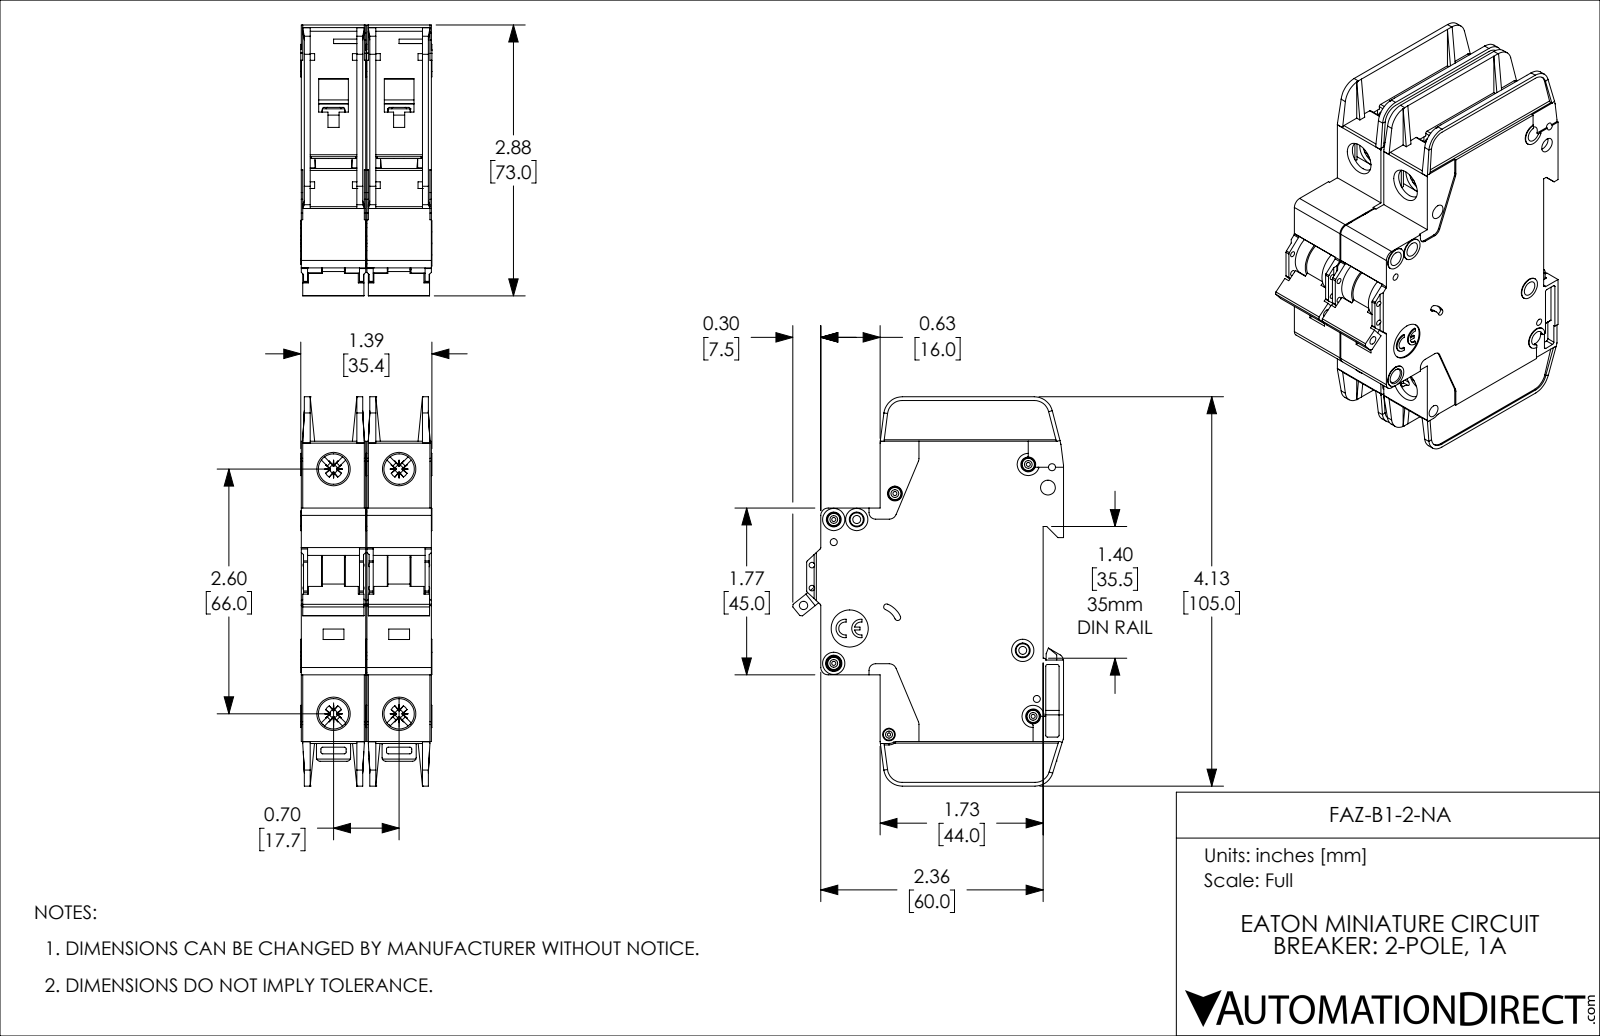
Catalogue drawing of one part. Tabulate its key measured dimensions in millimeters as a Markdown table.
| quantity | value |
| --- | --- |
| part name | FAZ-B1-2-NA |
| STEP written by | SolidWorks 2019 (AUTOMOTIVE_DESIGN) |
| units | millimeters |
| bodies | 2 solids, 2254 faces (1342 planar, 714 cylindrical, 198 other) |
| overall size | 105 × 73.1 × 35.4 |
| volume | 153 500 mm³ |
| surface area | 52 910 mm² |
| round holes (diameter × count) | 4 × 8, 1.1 × 5, 1.9 × 4, 8.2 × 4, 1.5 × 2, 2.2 × 2, 0.9 × 1, 2.3 × 1, 2.5 × 1, 3.4 × 1, 10 × 1 |
| round bosses / shafts (diameter × count) | 3.3 × 5, 6 × 4, 3 × 3, 2.5 × 2 |
| partial cylindrical surfaces (radius × count) | 0.5 × 57, 0.4 × 20, 1 × 14, 2 × 10, 1.1 × 8, 0.2 × 5, 5 × 5, 0.3 × 4 |
| main face-to-face distances | 17.7, 1.2, 17.4, 15, 2.4, 16.2, 13.8, 35.1, 18.9, 16.5 |
| hole center spacings | 6.2, 13.6, 17.7, 22.1, 66, 68.3, 4.8, 5.1 |
